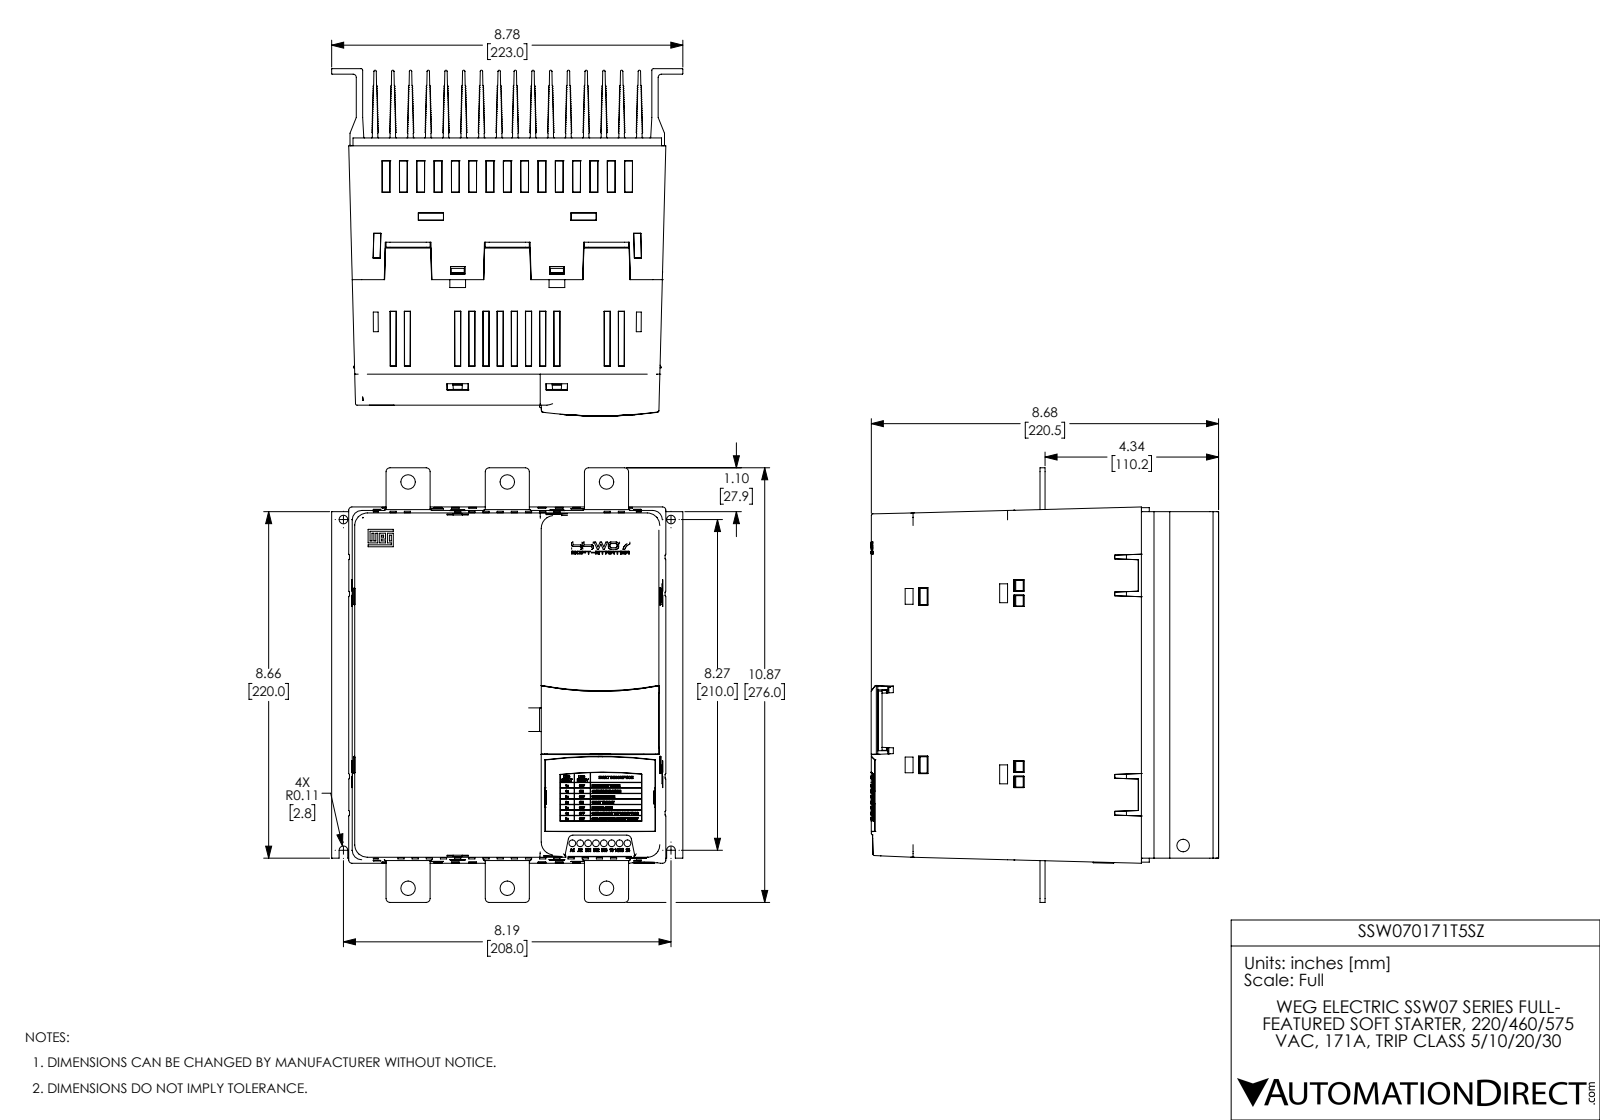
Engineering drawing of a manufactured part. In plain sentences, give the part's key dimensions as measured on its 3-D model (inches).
The part is named "SSW07 MEC C h1 ext1 Coord 1". Its 3-D file was written by "SolidWorks 2017 (AUTOMOTIVE_DESIGN)". It is 1 solid with 6371 faces: 2722 planar, 2638 cylindrical and 1011 other. Overall it measures 10.866 by 8.78 by 8.686 inches. Its volume is 494.2 cubic inches and its surface area 1 044 square inches. Round holes: 6 of diameter 0.362, 2 of diameter 0.217, 1 of diameter 0.315, 1 of diameter 0.453. Round bosses or shafts: 1 of diameter 0.512. Partial cylindrical surfaces (rounded edges, fillets, slot ends): 1440 of radius 0.016, 41 of radius 0.02, 16 of radius 0.008, 16 of radius 0.03, 12 of radius 0.098, 10 of radius 0.039, 8 of radius 0.102, 5 of radius 0.024. The main face-to-face distances are 1.33, 0.443, 0.886, 3.505, 8.861, 3.062, 1.773, 6.68, 4.391, 2.176. The hole center spacings are 2.48, 10.456, 10.157, 4.961, 11.304, 1.867, 1.869, 4.2.
